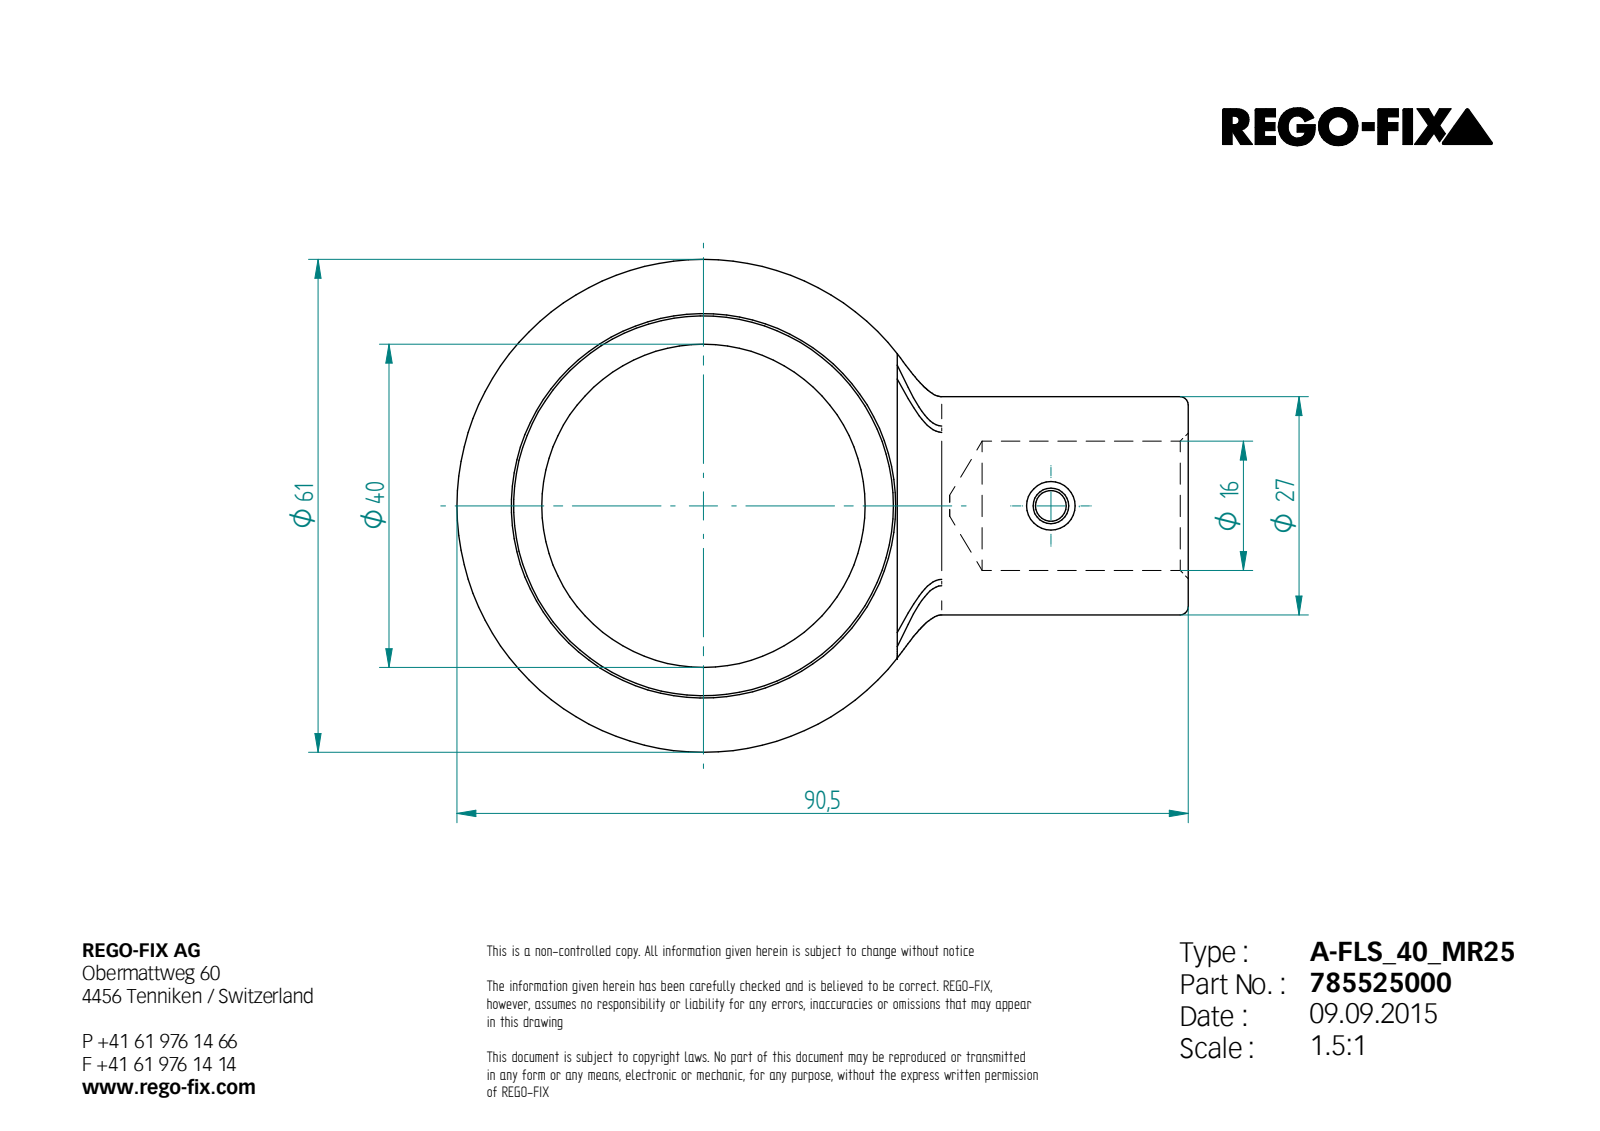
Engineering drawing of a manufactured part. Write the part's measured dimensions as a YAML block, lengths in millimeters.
part_name: "0007000; 0006879; 0006880; 0006993"
step_written_by: "Unknown (AUTOMOTIVE_DESIGN)"
units: millimeters
bodies: {solids: 4, faces: 140, planar: 88, cylindrical: 15, other: 37}
overall_size: [90.5, 61, 29.5]
volume: 44042
surface_area: 19201
round_holes:
  - {diameter: 4.5, count: 1}
  - {diameter: 5.5, count: 1}
  - {diameter: 16, count: 1}
  - {diameter: 40, count: 1}
  - {diameter: 47, count: 1}
round_bosses_or_shafts:
  - {diameter: 27, count: 1}
  - {diameter: 5.2, count: 1}
  - {diameter: 4.4, count: 1}
  - {diameter: 3.5, count: 1}
partial_cylinders:
  - {radius: 4, count: 1}
  - {radius: 21.35, count: 1}
  - {radius: 21.65, count: 1}
face_to_face_distances: [20, 6, 26, 2.5, 3.5, 23.5, 1, 1.5, 5, 25]
hole_center_spacings: [43]
